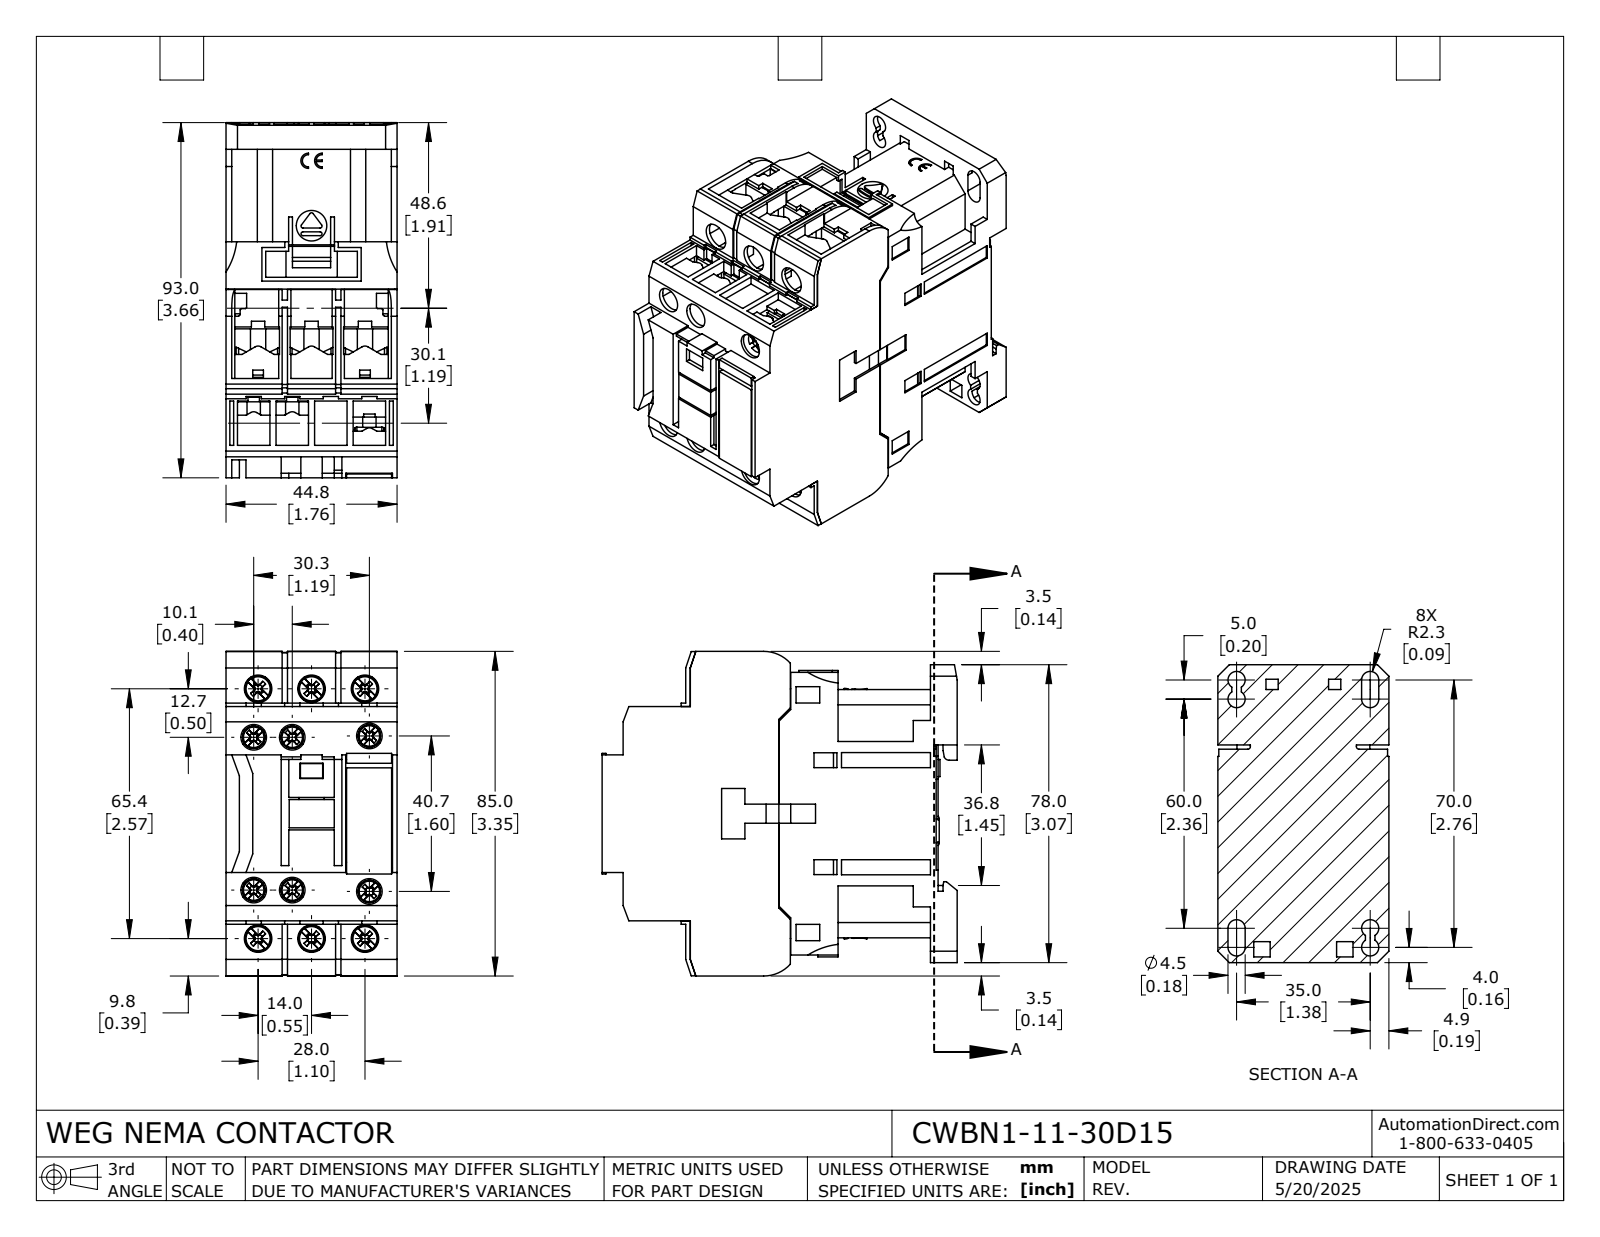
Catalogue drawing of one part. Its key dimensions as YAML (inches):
part_name: "CWBN1-11-30D15"
step_written_by: "SolidWorks 2024 (AUTOMOTIVE_DESIGN)"
units: inches
bodies: {solids: 42, faces: 2540, planar: 1924, cylindrical: 437, other: 179}
overall_size: [3.661, 3.346, 1.764]
volume: 14.55
surface_area: 115.4
round_holes:
  - {diameter: 0.124, count: 6}
  - {diameter: 0.142, count: 6}
  - {diameter: 0.264, count: 6}
  - {diameter: 0.283, count: 6}
  - {diameter: 0.177, count: 4}
round_bosses_or_shafts:
  - {diameter: 0.201, count: 6}
  - {diameter: 0.169, count: 6}
  - {diameter: 0.157, count: 6}
  - {diameter: 0.138, count: 6}
  - {diameter: 0.107, count: 6}
partial_cylinders:
  - {radius: 0.02, count: 34}
  - {radius: 0.028, count: 24}
  - {radius: 0.071, count: 12}
  - {radius: 0.081, count: 12}
  - {radius: 0.964, count: 12}
  - {radius: 1.079, count: 12}
  - {radius: 2.128, count: 12}
  - {radius: 3.127, count: 12}
face_to_face_distances: [1.764, 0.047, 0.132, 1.754, 0.024, 1.622, 1.717, 3.445, 0.059, 0.071]
hole_center_spacings: [0.551, 2.633, 2.575, 0.165, 0.174, 0.197, 0.398, 0.488]
